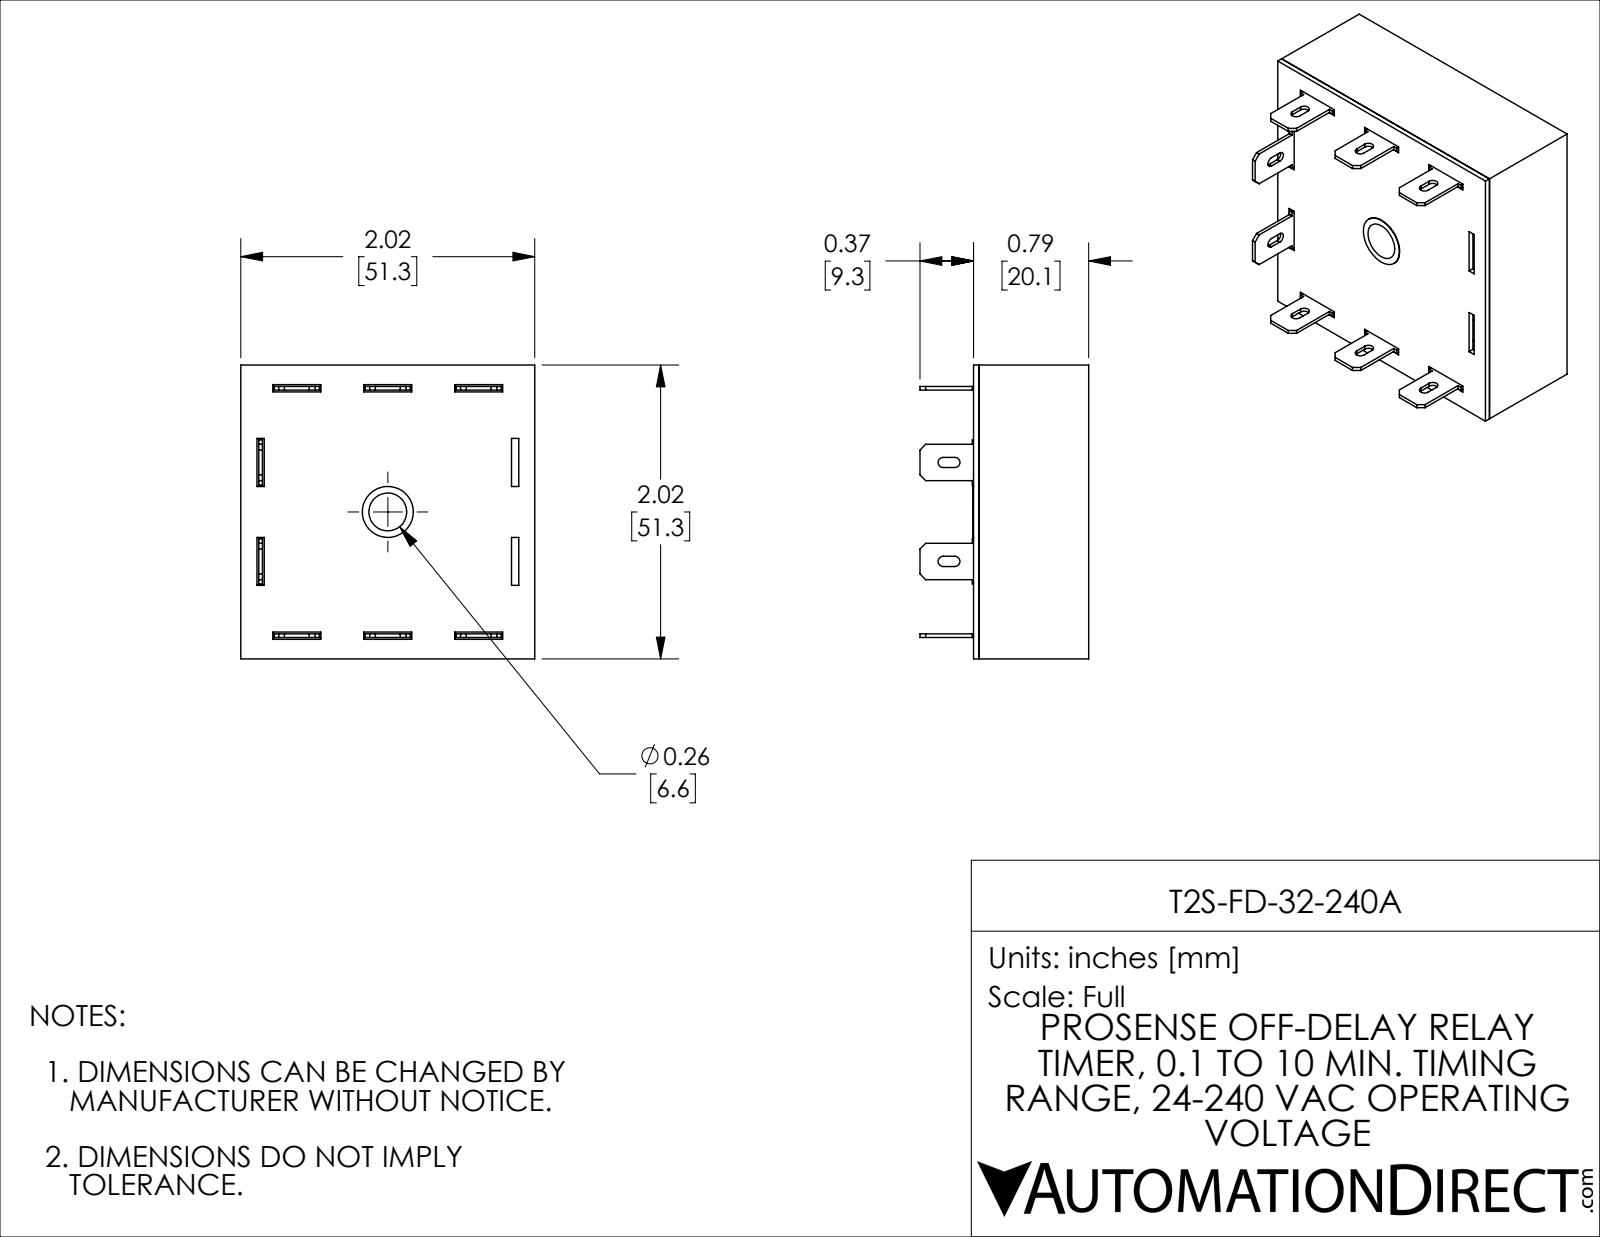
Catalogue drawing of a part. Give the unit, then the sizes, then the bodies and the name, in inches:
Units: inches
Overall size (bounding box): 2.02 × 2.02 × 1.16
Round holes (diameter × count): ⌀0.35 ×1
Partial cylindrical surfaces — rounded edges, fillets, slot ends (radius × count): R0.035 ×10
Main face-to-face distances: 0.045, 1.975, 0.754, 0.792, 0.038, 0.709, 0.747, 2.02, 1.93, 0.147
Volume: 0.674 in³ · Surface area: 35.37 in²
Bodies: 10 solids, 256 faces (234 planar, 20 cylindrical, 2 other)
Part name (STEP PRODUCT): T2S-FD-32-240A
STEP written by: SolidWorks 2021 (CONFIG_CONTROL_DESIGN)
